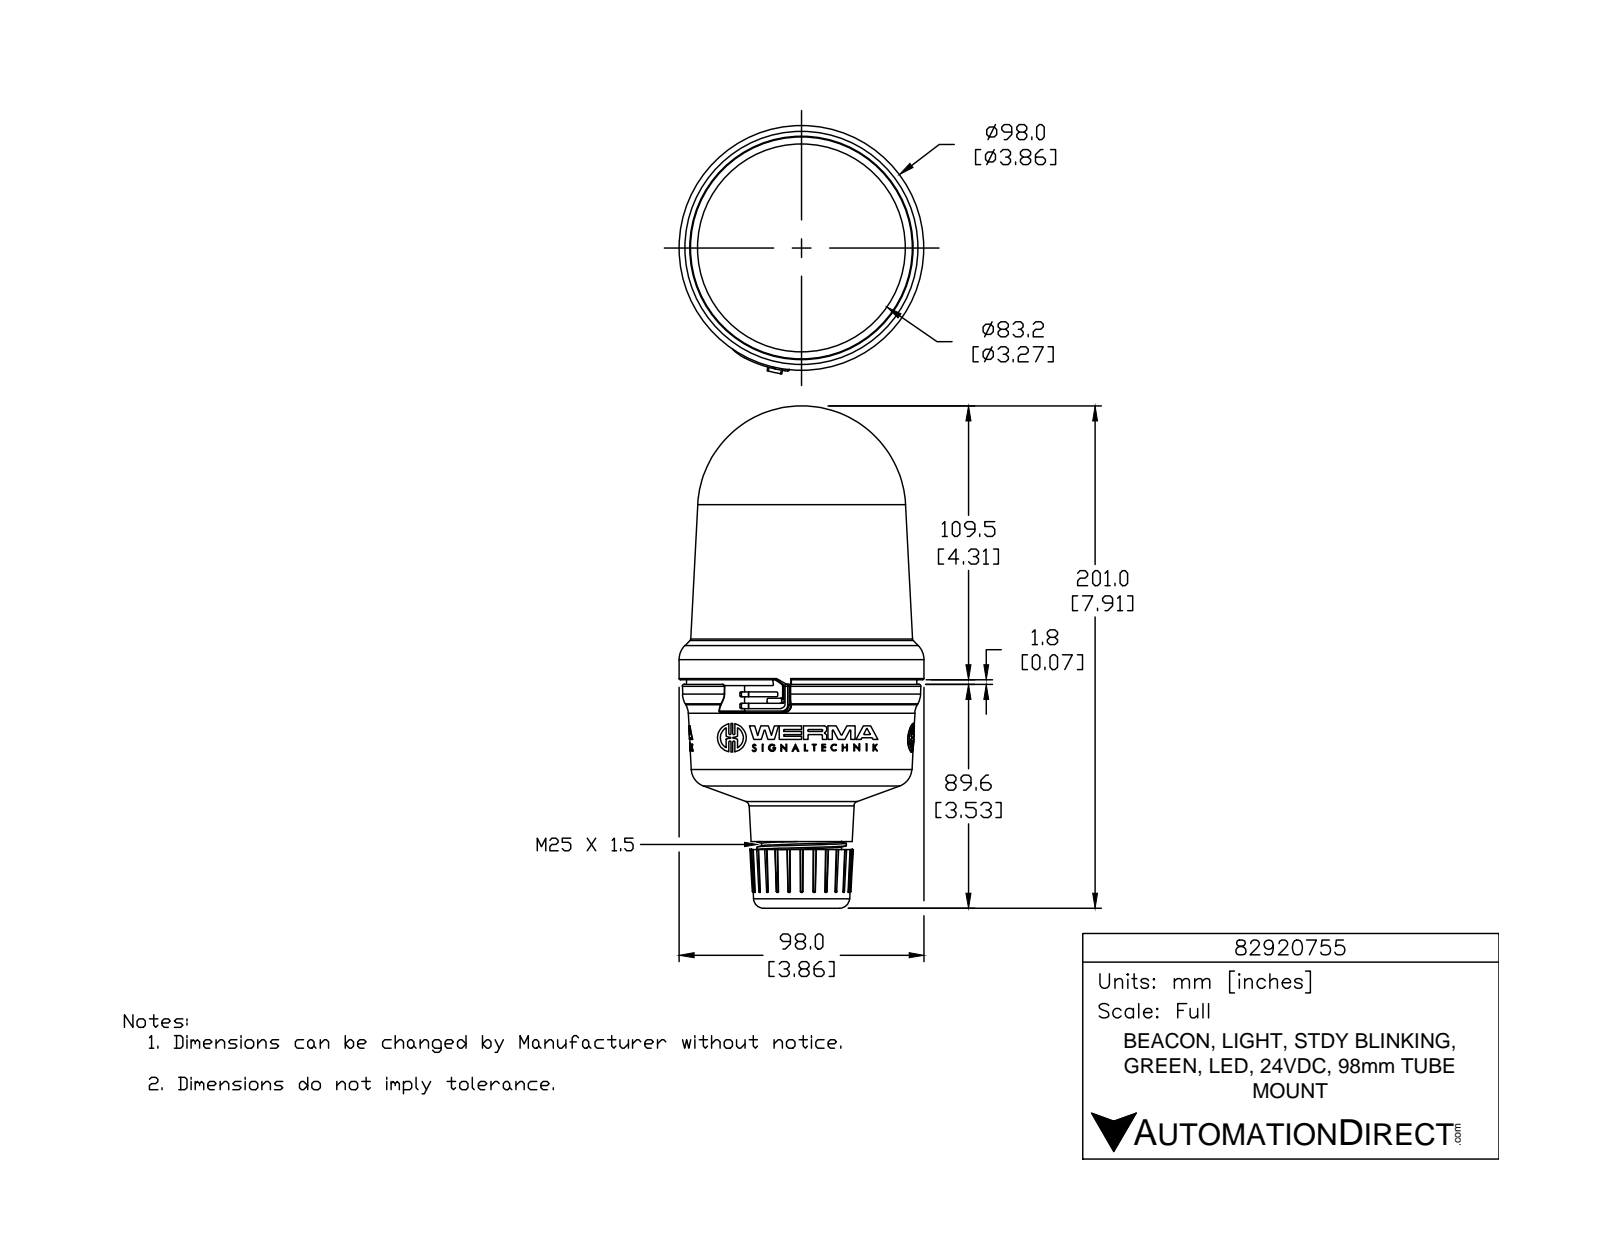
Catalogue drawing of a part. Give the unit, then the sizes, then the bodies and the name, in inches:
Units: inches
Overall size (bounding box): 7.914 × 3.912 × 3.858
Round holes (diameter × count): ⌀0.078 ×3, ⌀1.013 ×1, ⌀1.024 ×1
Round bosses / shafts (diameter × count): ⌀0.452 ×3, ⌀0.113 ×3, ⌀3.858 ×1, ⌀1.409 ×1, ⌀1.261 ×1
Partial cylindrical surfaces — rounded edges, fillets, slot ends (radius × count): R0.02 ×12, R0.007 ×9, R0.007 ×6, R0.016 ×6, R0.016 ×6, R0.016 ×6, R0.262 ×6, R0.006 ×3
Main face-to-face distances: 2.214, 0.462, 2.676, 0.335, 0.127, 2.548, 2.603, 2.476, 2.141, 0.073
Volume: 54.7 in³ · Surface area: 91.39 in²
Bodies: 1 solid, 1006 faces (554 planar, 189 cylindrical, 263 other)
Part name (STEP PRODUCT): 82920755
STEP written by: SolidWorks 2015 (AUTOMOTIVE_DESIGN)
